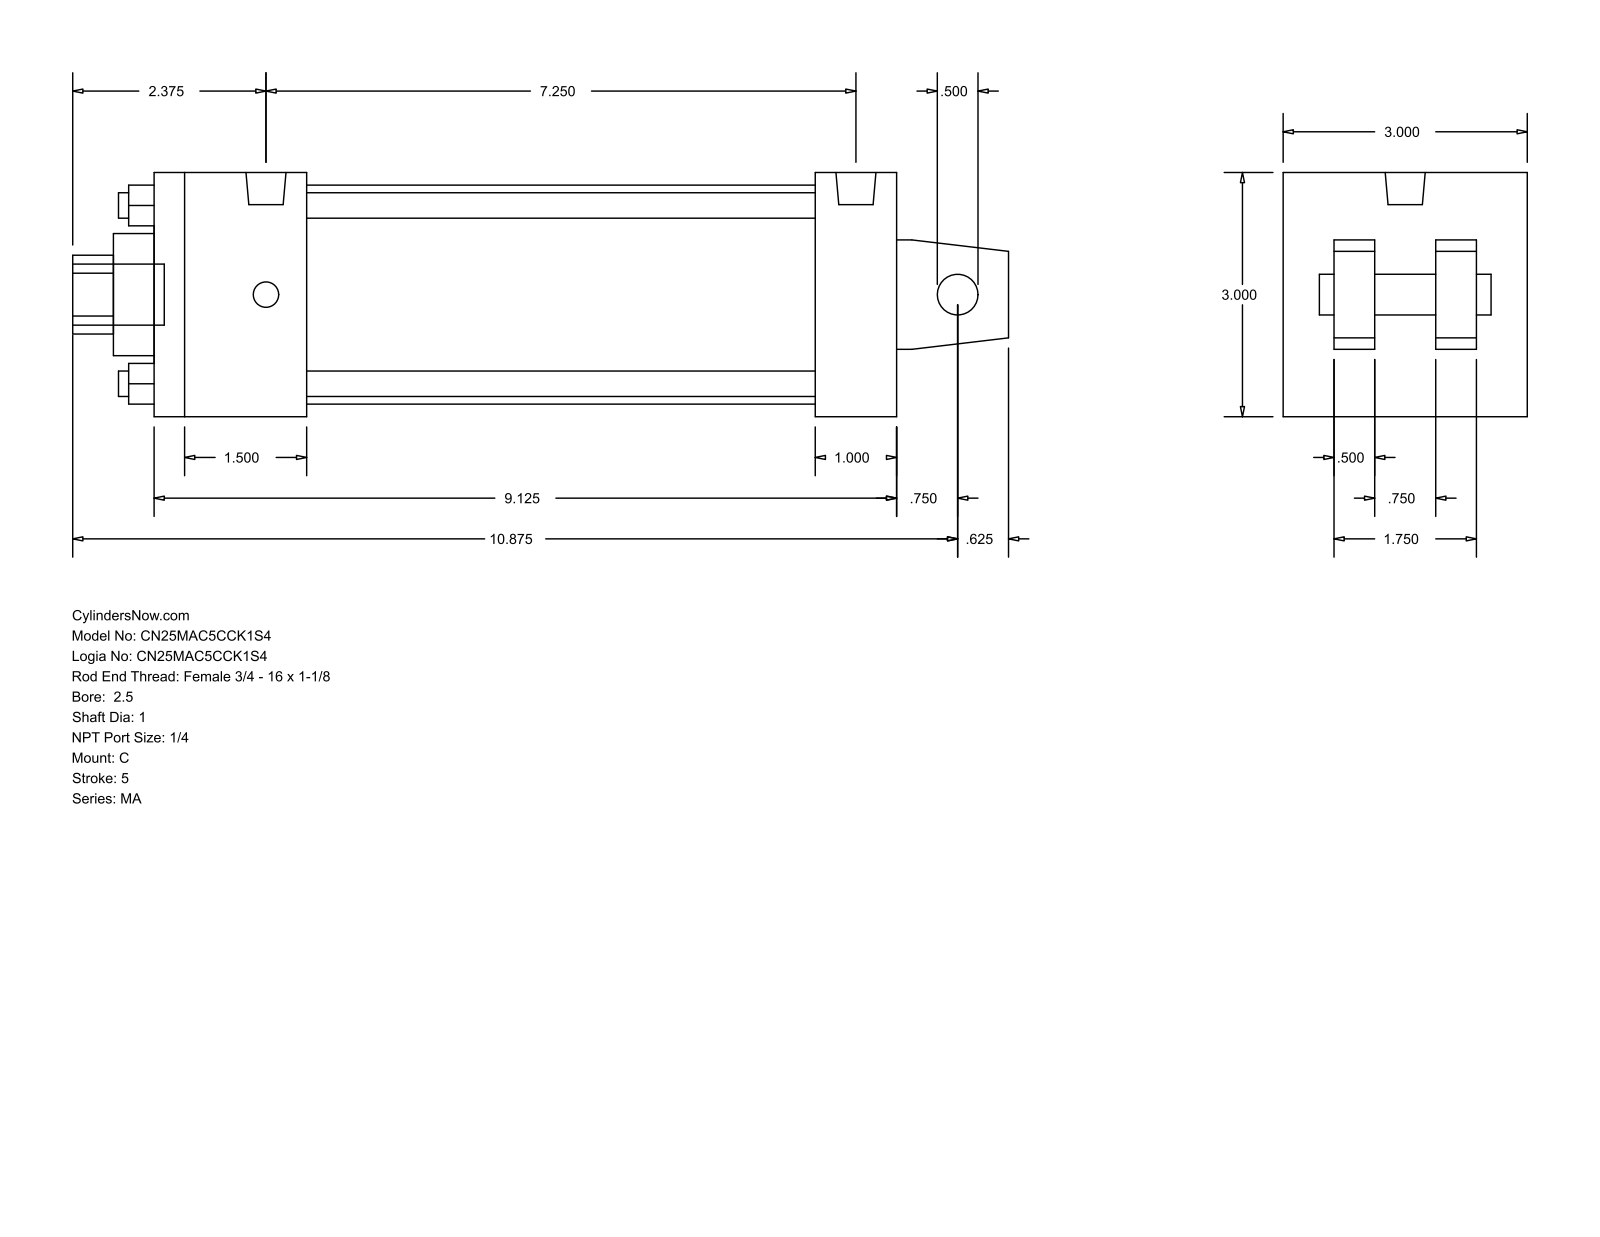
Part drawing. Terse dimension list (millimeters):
name: MA_C__0250_1
written by: GSSL Pune (CONFIG_CONTROL_DESIGN)
unit: mm
bodies: 0 solids, 103 faces (76 planar, 27 cylindrical, 0 other)
size: 292.1 × 76.2 × 76.2
holes: 4× ⌀7.94, 1× ⌀12.7, 1× ⌀25.4, 1× ⌀38.1, 1× ⌀68.33
bosses: 4× ⌀7.94, 2× ⌀12.49, 1× ⌀19.05
rounds: 1× R12.29
face distances: 76.2, 231.78, 47.63, 12.7, 15.87, 60.33, 25.4, 28.57, 206.38, 158.75
hole spacings: 39.33, 55.62, 78.66
